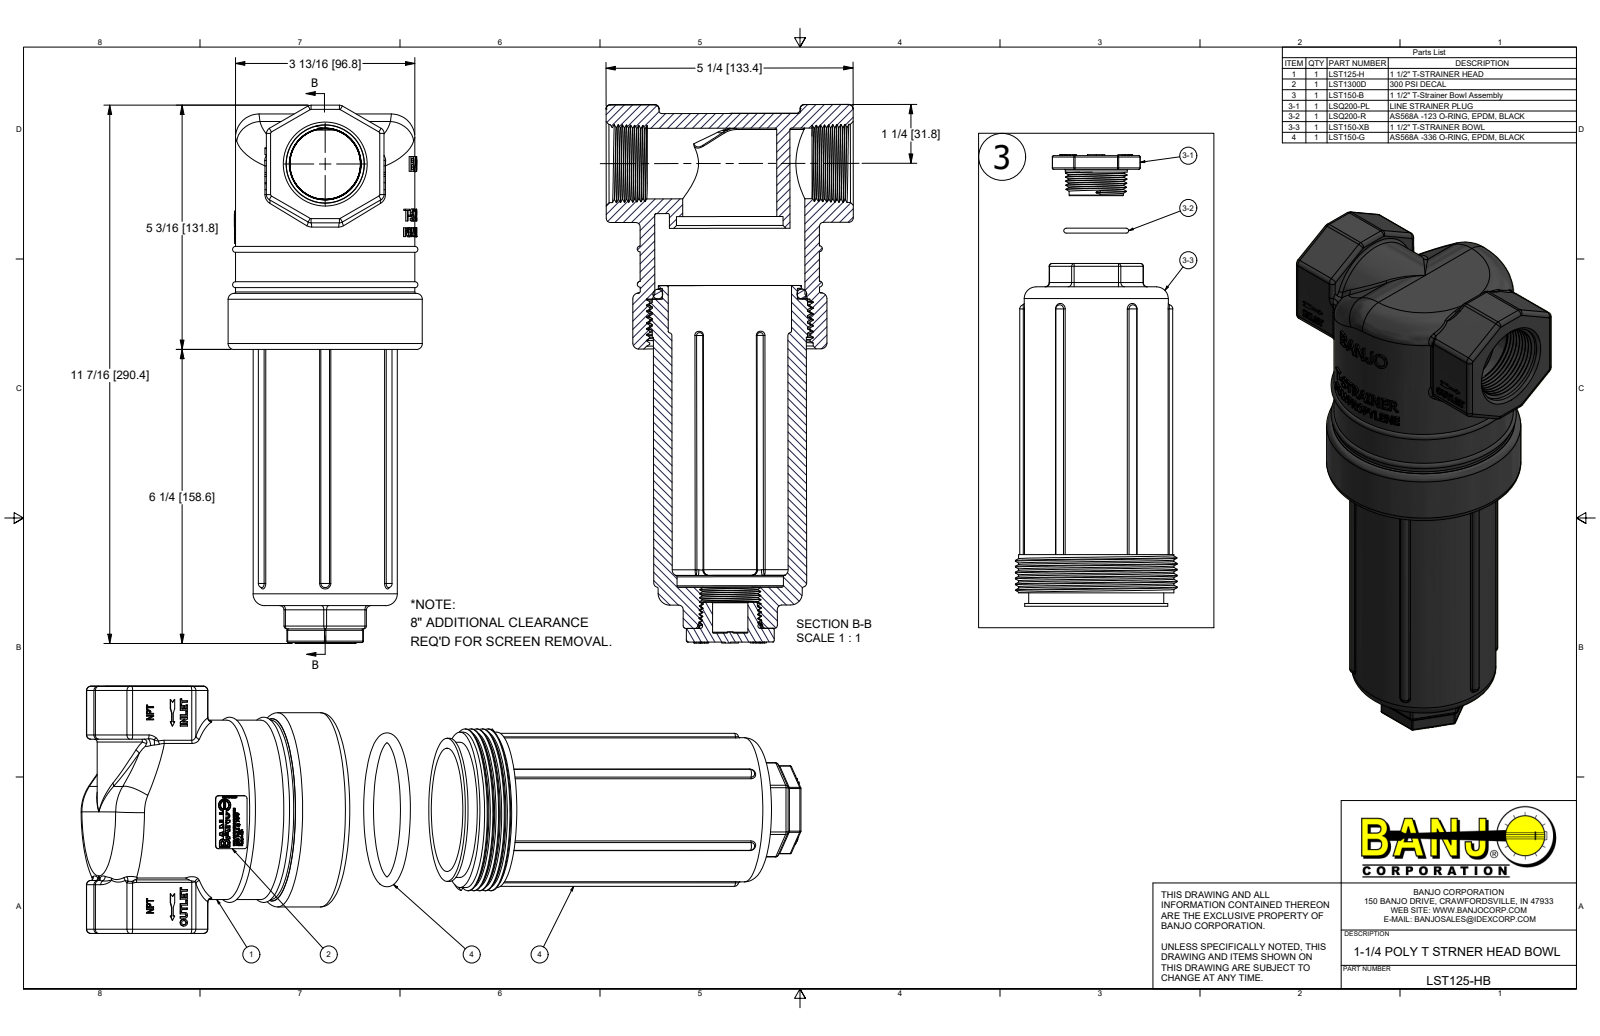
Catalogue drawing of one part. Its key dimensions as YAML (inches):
part_name: "LST125-HB; CE050D; LST125-H; LST1300D (+5 more)"
step_written_by: "Autodesk Inventor 2018 (AUTOMOTIVE_DESIGN)"
units: inches
bodies: {solids: 7, faces: 2812, planar: 1509, cylindrical: 269, other: 1034}
overall_size: [48.286, 11.433, 4.125]
volume: 47.5
surface_area: 637.8
round_holes:
  - {diameter: 0.181, count: 1}
  - {diameter: 0.257, count: 1}
  - {diameter: 0.75, count: 1}
  - {diameter: 1.5, count: 1}
  - {diameter: 2, count: 1}
  - {diameter: 2.26, count: 1}
  - {diameter: 2.265, count: 1}
  - {diameter: 2.62, count: 1}
  - {diameter: 3.19, count: 1}
  - {diameter: 3.403, count: 1}
  - {diameter: 3.54, count: 1}
round_bosses_or_shafts:
  - {diameter: 4.125, count: 1}
  - {diameter: 3.81, count: 1}
  - {diameter: 3.435, count: 1}
  - {diameter: 3.3, count: 1}
  - {diameter: 3.063, count: 1}
  - {diameter: 3.04, count: 1}
  - {diameter: 2.87, count: 1}
  - {diameter: 2.563, count: 1}
partial_cylinders:
  - {radius: 0.03, count: 44}
  - {radius: 0.09, count: 34}
  - {radius: 0.06, count: 16}
  - {radius: 0.125, count: 10}
  - {radius: 0.078, count: 6}
  - {radius: 0.094, count: 6}
  - {radius: 0.026, count: 2}
  - {radius: 0.033, count: 2}
face_to_face_distances: [2.5, 3.94, 6.12, 10.06, 9.748, 3.628, 0.313, 5.25, 0.38, 6.5]
